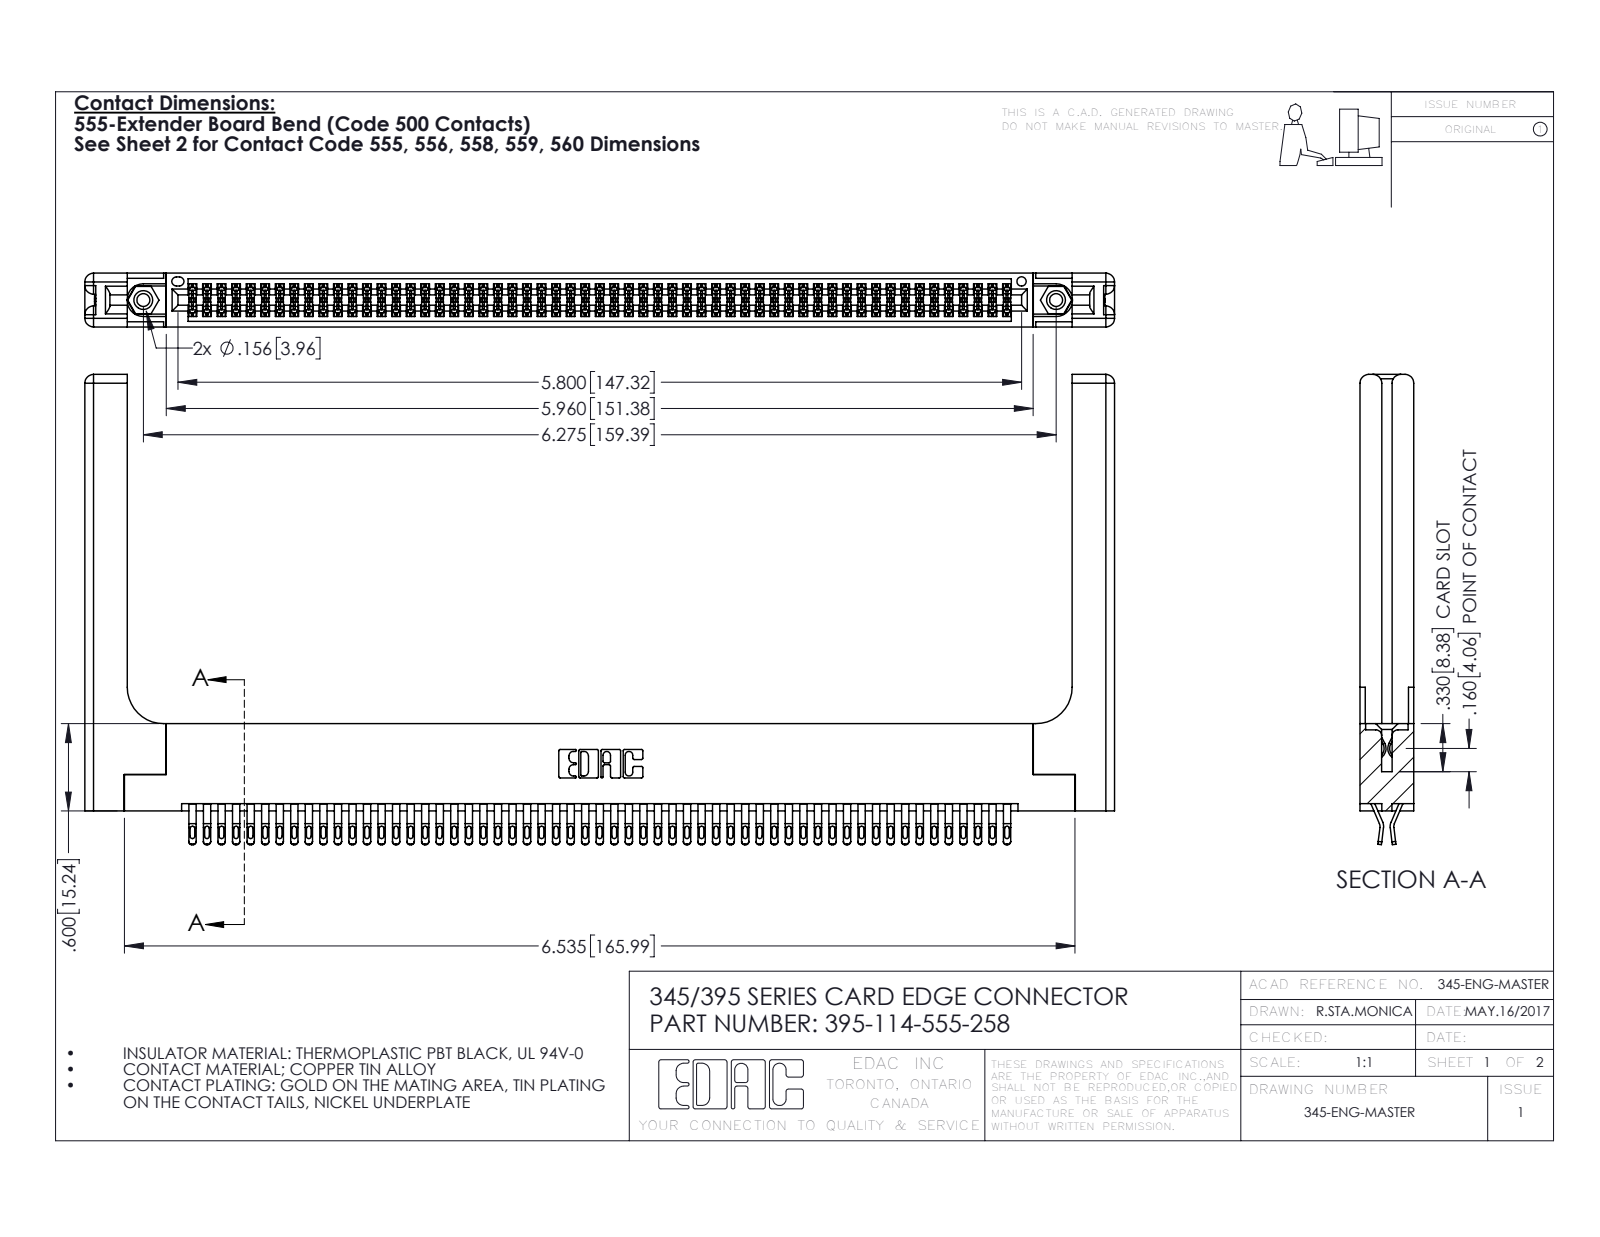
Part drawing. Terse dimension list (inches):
name: 395-114-555-258; 345-220-058_345-220-058; 345-250-001_345-250-001-102; 345 Part_Flush Mounting Lugs - 0.156 Dia-TH (+1 more)
written by: SolidWorks 2016 (CONFIG_CONTROL_DESIGN)
unit: in
bodies: 119 solids, 6766 faces (3762 planar, 2944 cylindrical, 60 other)
size: 7.079 × 3.232 × 0.37
volume: 1.612 in³; area: 51.17 in²
holes: 2× ⌀0.089, 2× ⌀0.125, 2× ⌀0.156, 1× ⌀0.064
bosses: 2× ⌀0.155
rounds: 285× R0.016, 228× R0.02, 171× R0.006, 22× R0.01, 16× R0.06, 6× R0.007, 6× R0.031, 3× R0.026
face distances: 0.072, 0.298, 0.37, 0.025, 0.2, 0.098, 0.272, 0.225, 0.148, 0.15
hole spacings: 0.27, 6.039, 6.275
